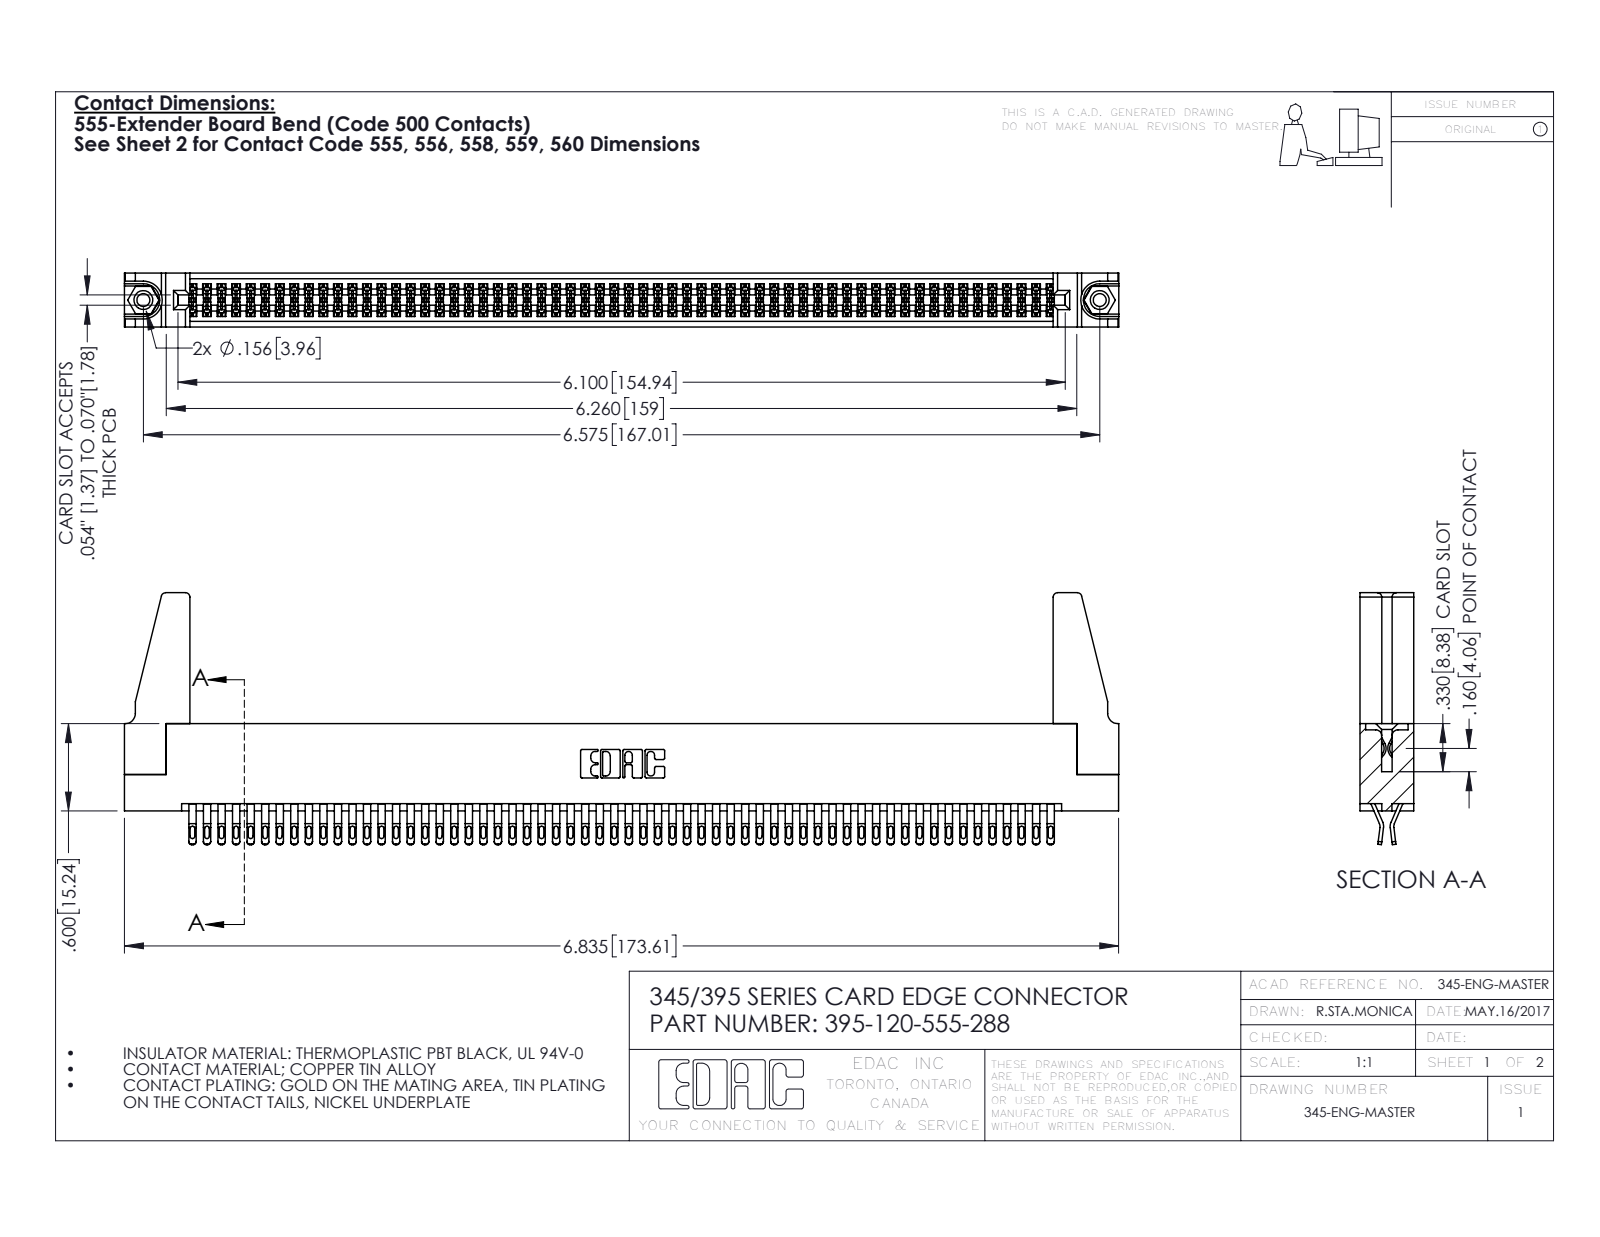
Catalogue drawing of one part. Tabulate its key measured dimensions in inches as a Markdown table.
| quantity | value |
| --- | --- |
| part name | 345-220-078_345-220-088; 345-250-001_345-250-001-102; 345-292-001_555 Tail; 395-120-555-288 (+1 more) |
| STEP written by | SolidWorks 2016 (CONFIG_CONTROL_DESIGN) |
| units | inches |
| bodies | 125 solids, 6970 faces (3872 planar, 3082 cylindrical, 16 other) |
| overall size | 6.836 × 1.732 × 0.37 |
| volume | 1.259 in³ |
| surface area | 47.08 in² |
| round holes (diameter × count) | 0.089 × 2, 0.125 × 2, 0.156 × 2, 0.064 × 1 |
| round bosses / shafts (diameter × count) | 0.155 × 2 |
| partial cylindrical surfaces (radius × count) | 0.016 × 300, 0.02 × 240, 0.006 × 180, 0.01 × 22, 0.03 × 8, 0.007 × 6, 0.031 × 6, 0.026 × 3 |
| main face-to-face distances | 0.072, 0.298, 0.37, 0.025, 0.2, 0.098, 0.272, 0.225, 0.175, 0.149 |
| hole center spacings | 0.27, 6.339, 6.575 |
